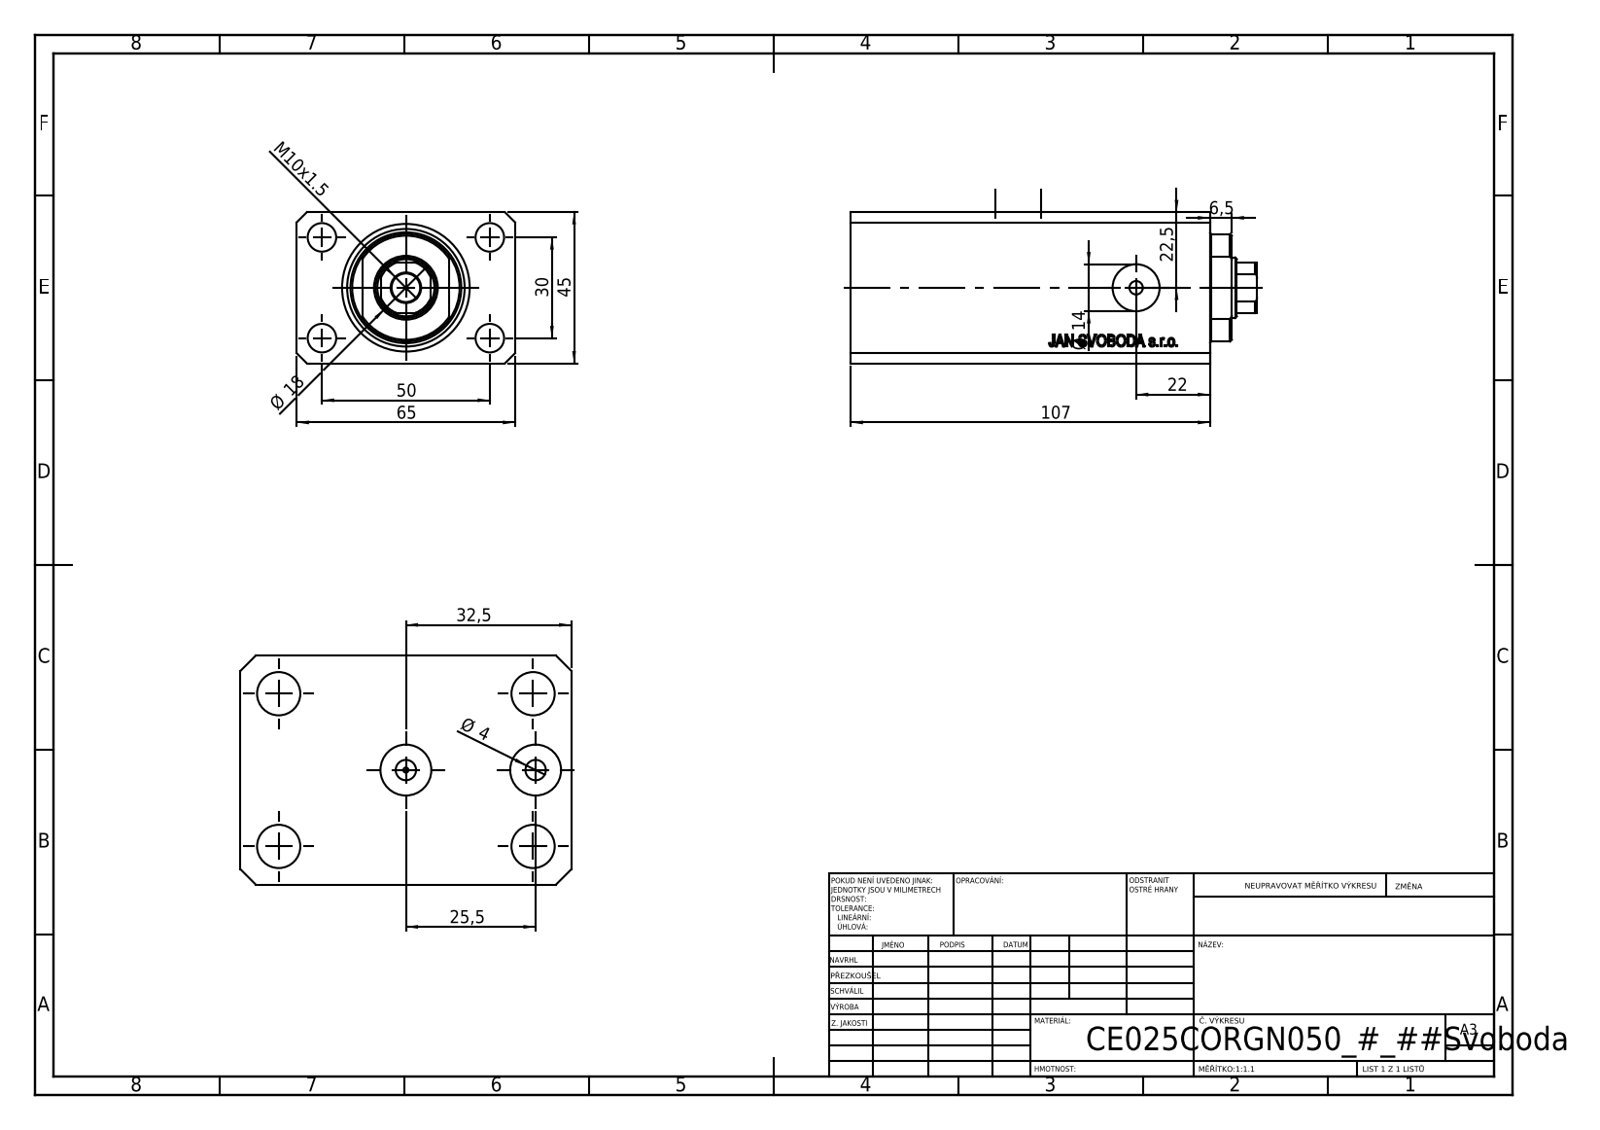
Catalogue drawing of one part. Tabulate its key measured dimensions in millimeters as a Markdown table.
| quantity | value |
| --- | --- |
| part name | V250CE_C_VCP; V250CE_VC_C; V250CE_C_Body |
| STEP written by | SolidWorks 2019 (CONFIG_CONTROL_DESIGN) |
| units | millimeters |
| bodies | 3 solids, 868 faces (428 planar, 46 cylindrical, 394 other) |
| overall size | 121 × 65 × 45 |
| volume | 276 706 mm³ |
| surface area | 64 464 mm² |
| round holes (diameter × count) | 8.5 × 5, 4 × 4, 10 × 2, 14 × 2, 1.25 × 1, 18 × 1, 25 × 1, 38 × 1 |
| partial cylindrical surfaces (radius × count) | 8.5 × 1, 16 × 1 |
| main face-to-face distances | 45, 65, 14, 107, 93, 6.9, 86.1, 100.1, 73.52, 20.5 |
| hole center spacings | 29.15, 15.01, 30, 50, 52.68, 58.31, 25.5, 63 |
